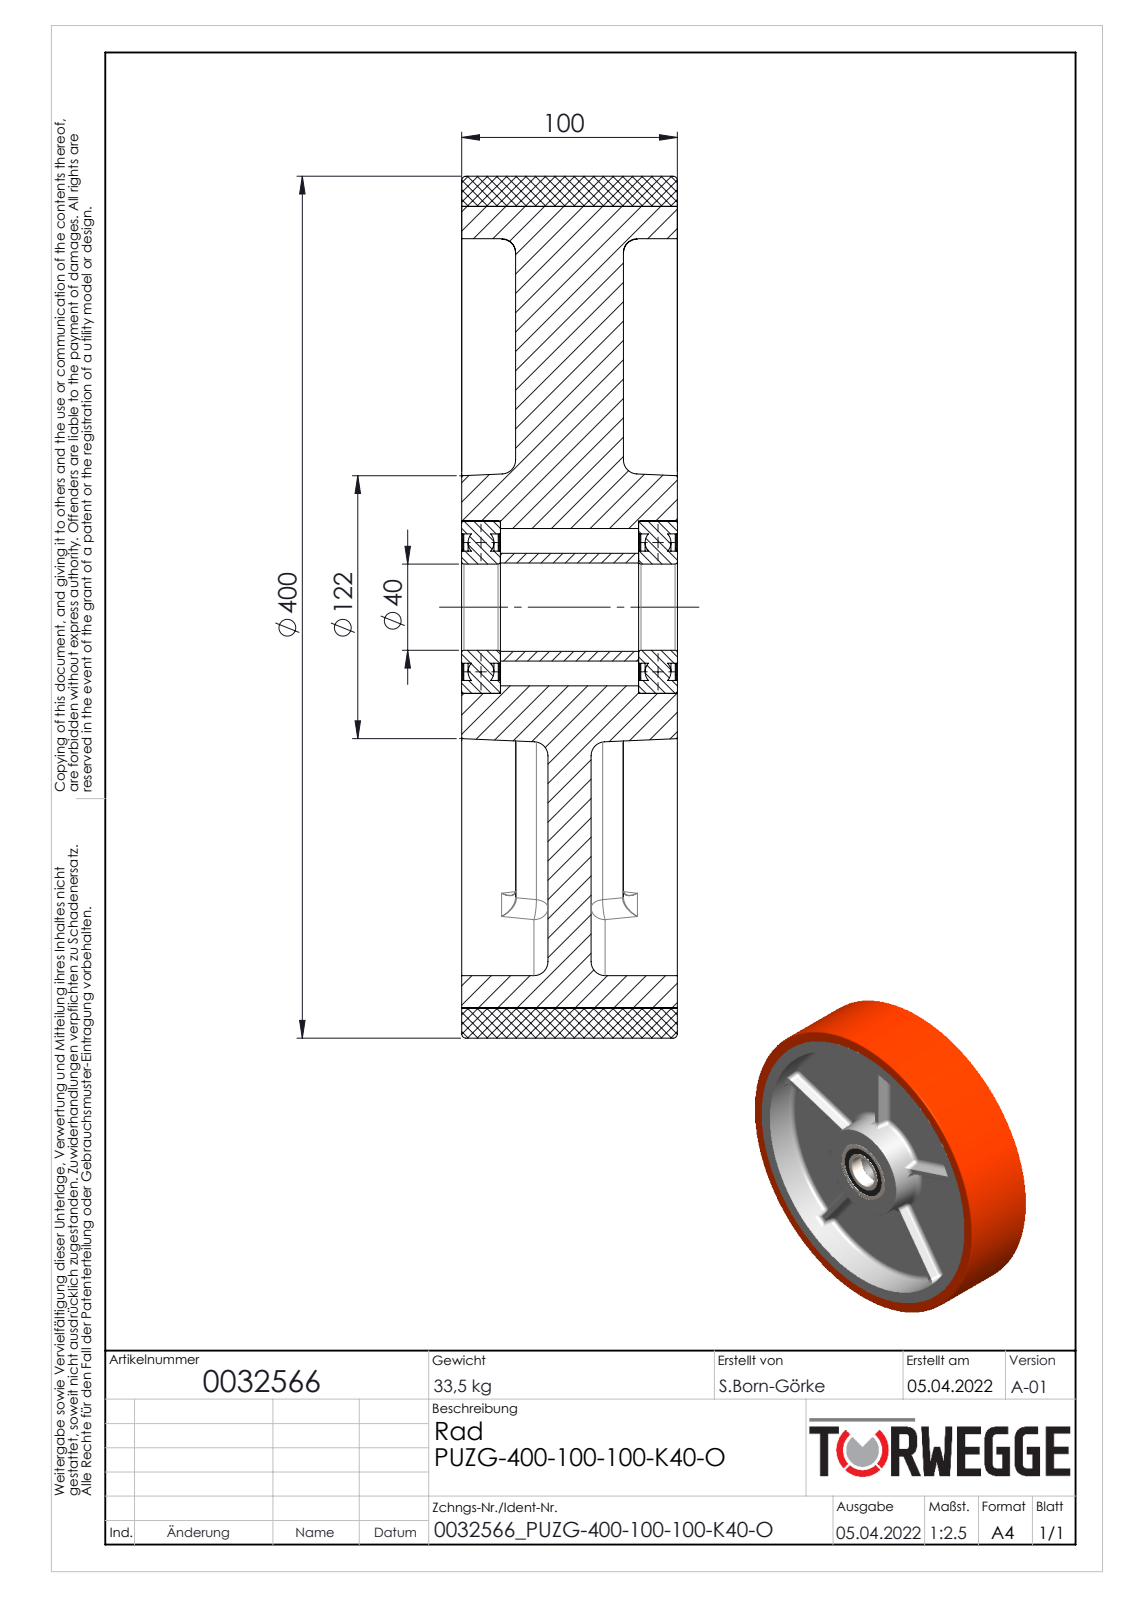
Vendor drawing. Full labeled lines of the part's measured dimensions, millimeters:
Part name (STEP PRODUCT): 0032566
STEP written by: SolidWorks 2020 (AUTOMOTIVE_DESIGN)
Units: millimetres
Bodies: 5 solids, 410 faces (66 planar, 100 cylindrical, 244 other)
Overall size (bounding box): 400 × 400 × 100.1
Volume: 6 082 000 mm³ · Surface area: 816 828 mm²
Round holes (diameter × count): ⌀40 ×1, ⌀41 ×1, ⌀68 ×1, ⌀73 ×1, ⌀80 ×1, ⌀342 ×1, ⌀372 ×1
Round bosses / shafts (diameter × count): ⌀400 ×1, ⌀52 ×1, ⌀50 ×1
Partial cylindrical surfaces — rounded edges, fillets, slot ends (radius × count): R0.5 ×20, R6.5 ×20
Main face-to-face distances: 40, 60, 20, 100, 0.5, 82.1, 17, 15.3, 82.05, 17.5
